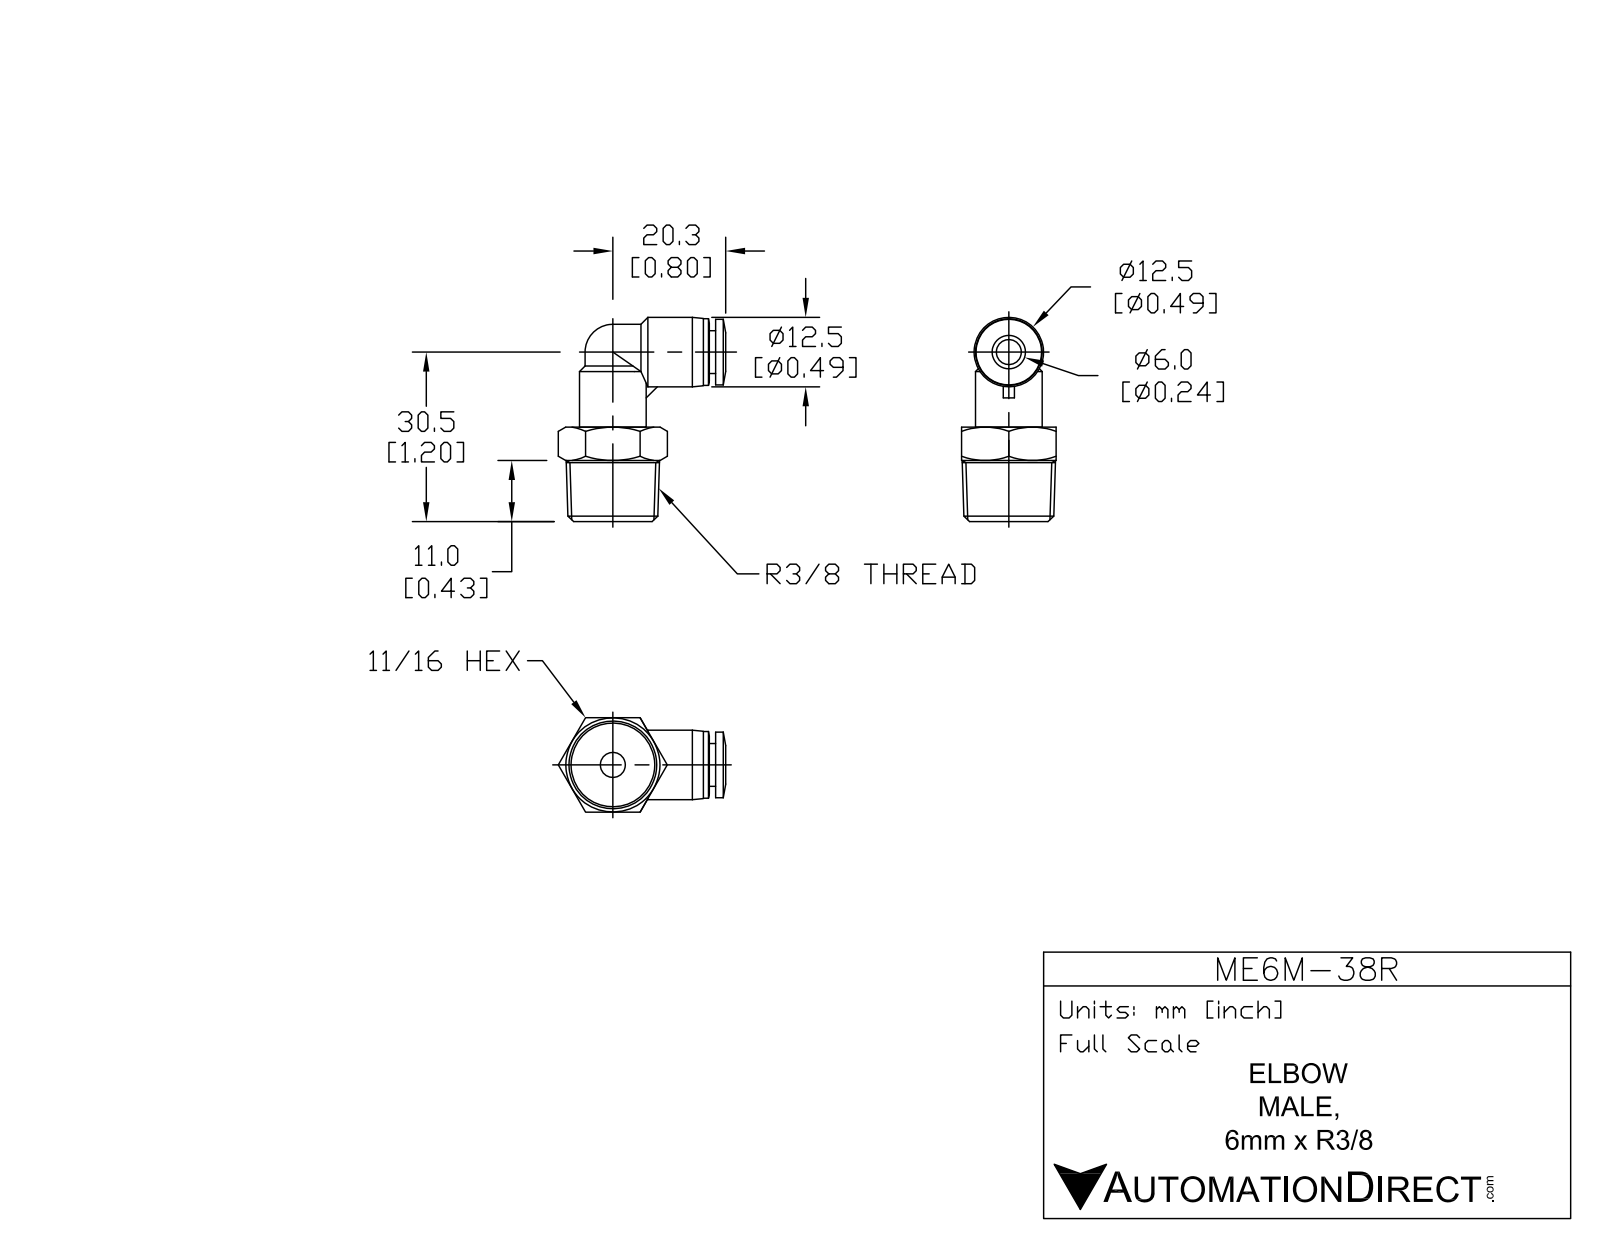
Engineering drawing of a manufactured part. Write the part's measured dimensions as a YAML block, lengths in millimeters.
part_name: "ME6M-38R"
step_written_by: "SolidWorks 2015 (AUTOMOTIVE_DESIGN)"
units: millimeters
bodies: {solids: 1, faces: 69, planar: 17, cylindrical: 19, other: 33}
overall_size: [36.8, 30.1, 17]
volume: 6340
surface_area: 3397
round_holes:
  - {diameter: 4, count: 2}
  - {diameter: 6.3, count: 1}
round_bosses_or_shafts:
  - {diameter: 12, count: 2}
  - {diameter: 12.5, count: 1}
  - {diameter: 11.8, count: 1}
  - {diameter: 7.7, count: 1}
partial_cylinders:
  - {radius: 5, count: 2}
face_to_face_distances: [17, 1.1, 13.5, 14.6, 11, 6, 7.5, 9.5, 16.4, 2.9]
